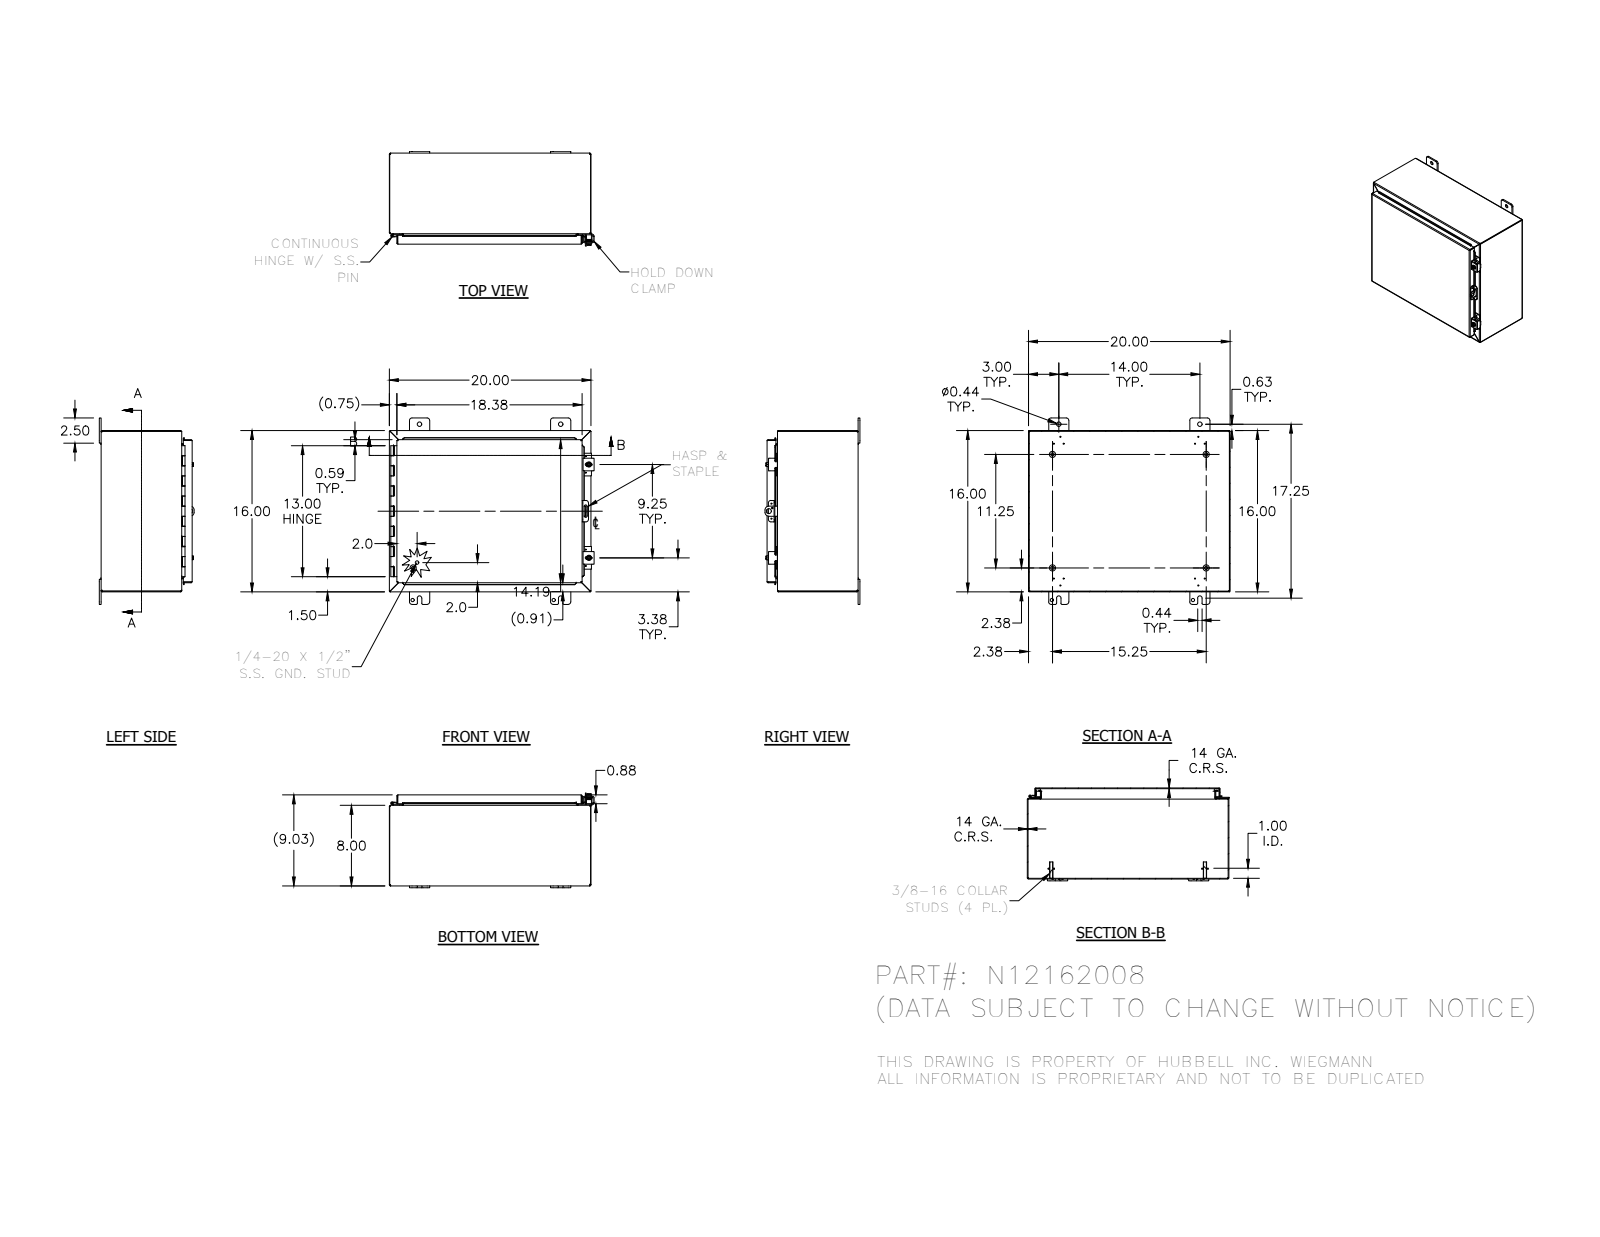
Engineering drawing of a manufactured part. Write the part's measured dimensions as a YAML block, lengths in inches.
part_name: "N12162008; 34840; 38420; N12162008BKP (+8 more)"
step_written_by: "Autodesk Inventor 2012 (AUTOMOTIVE_DESIGN)"
units: inches
bodies: {solids: 27, faces: 914, planar: 489, cylindrical: 308, other: 117}
overall_size: [20.311, 18.5, 9.41]
volume: 113.6
surface_area: 2945
round_holes:
  - {diameter: 0.12, count: 12}
  - {diameter: 0.11, count: 7}
  - {diameter: 0.313, count: 4}
  - {diameter: 0.438, count: 4}
  - {diameter: 0.211, count: 2}
  - {diameter: 0.281, count: 2}
  - {diameter: 0.3, count: 2}
  - {diameter: 0.125, count: 1}
  - {diameter: 0.156, count: 1}
  - {diameter: 0.5, count: 1}
round_bosses_or_shafts:
  - {diameter: 0.625, count: 4}
  - {diameter: 0.33, count: 4}
  - {diameter: 0.25, count: 4}
  - {diameter: 0.52, count: 2}
  - {diameter: 0.5, count: 2}
  - {diameter: 0.35, count: 2}
  - {diameter: 0.115, count: 2}
  - {diameter: 0.337, count: 1}
partial_cylinders:
  - {radius: 0.03, count: 27}
  - {radius: 0.063, count: 25}
  - {radius: 0.125, count: 25}
  - {radius: 0.25, count: 25}
  - {radius: 0.031, count: 23}
  - {radius: 0.105, count: 23}
  - {radius: 0.07, count: 8}
  - {radius: 0.1, count: 4}
face_to_face_distances: [0.074, 8.959, 15.926, 8.885, 9.033, 19.926, 7.926, 1.033, 16, 15.852]
hole_center_spacings: [14, 0.759, 0.839, 0.94, 0.969, 1.593, 1.995, 13.375]
